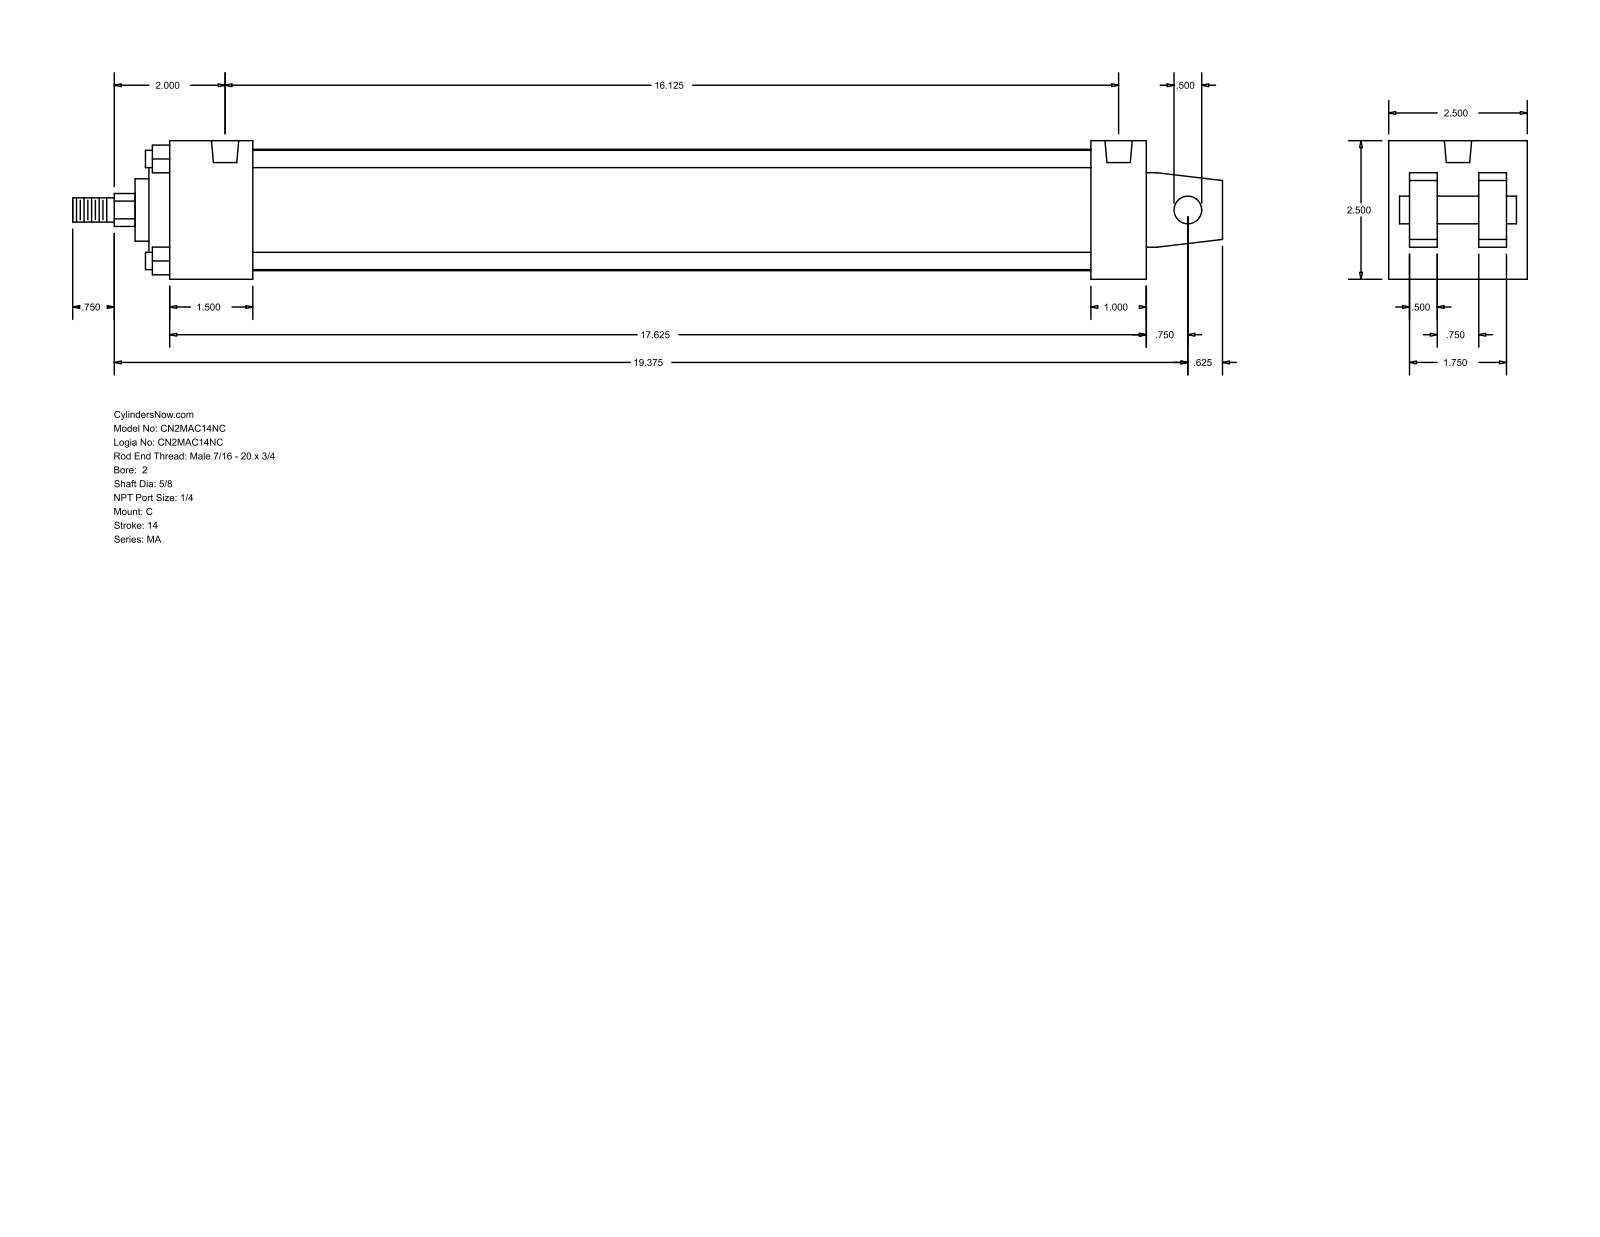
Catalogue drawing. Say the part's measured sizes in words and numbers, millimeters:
The part is named "MA_C__0200_0.625". Its 3-D file was written by "GSSL Pune (CONFIG_CONTROL_DESIGN)". It is 0 solids with 105 faces: 77 planar, 28 cylindrical and 0 other. Overall it measures 527.05 by 63.5 by 63.5 millimeters. Round holes: 4 of diameter 7.94, 2 of diameter 12.49. Round bosses or shafts: 4 of diameter 7.94, 1 of diameter 55.63, 1 of diameter 50.8, 1 of diameter 28.57, 1 of diameter 15.88, 1 of diameter 12.7, 1 of diameter 11.11. Partial cylindrical surfaces (rounded edges, fillets, slot ends): 1 of radius 7.54. The main face-to-face distances are 63.5, 9.52, 12.7, 22.22, 41.28, 53.98, 31.76, 38.1, 447.67, 409.57. The hole center spacings are 409.58.
